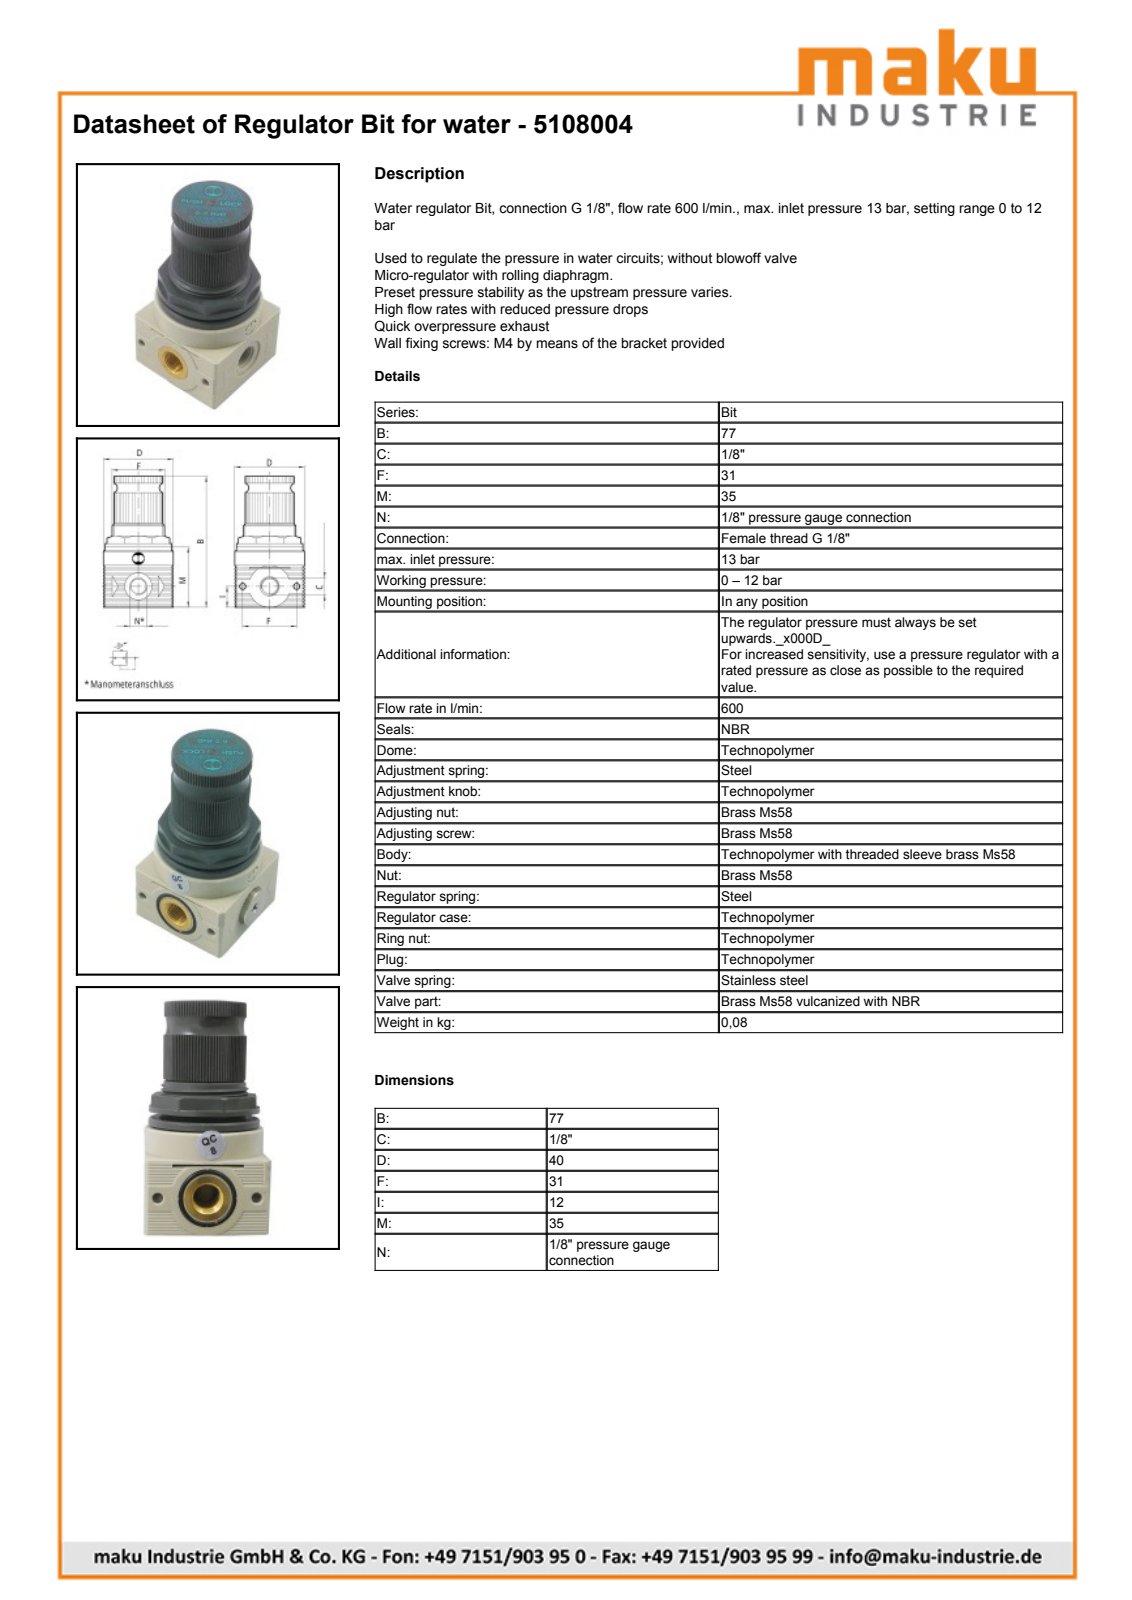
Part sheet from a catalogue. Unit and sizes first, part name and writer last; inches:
Units: inches
Overall size (bounding box): 3.031 × 1.634 × 1.575
Round holes (diameter × count): ⌀0.157 ×2, ⌀0.337 ×2, ⌀0.61 ×1
Round bosses / shafts (diameter × count): ⌀1.571 ×1, ⌀1.496 ×1, ⌀1.48 ×1, ⌀1.181 ×1, ⌀1.102 ×1, ⌀0.945 ×1, ⌀0.591 ×1, ⌀0.383 ×1
Partial cylindrical surfaces — rounded edges, fillets, slot ends (radius × count): R0.472 ×1
Main face-to-face distances: 1.26, 1.575, 0.039, 0.354, 0.394, 1.573, 3.031, 1.772, 1.535, 0.748
Hole centre spacings: 0.61, 1.22
Volume: 4.713 in³ · Surface area: 28.17 in²
Bodies: 3 solids, 127 faces (92 planar, 27 cylindrical, 8 other)
Part name (STEP PRODUCT): 5108004; 5108004-BD; 5108004-KN; 1/8-BIT
STEP written by: PARTsolutions (AUTOMOTIVE_DESIGN)
